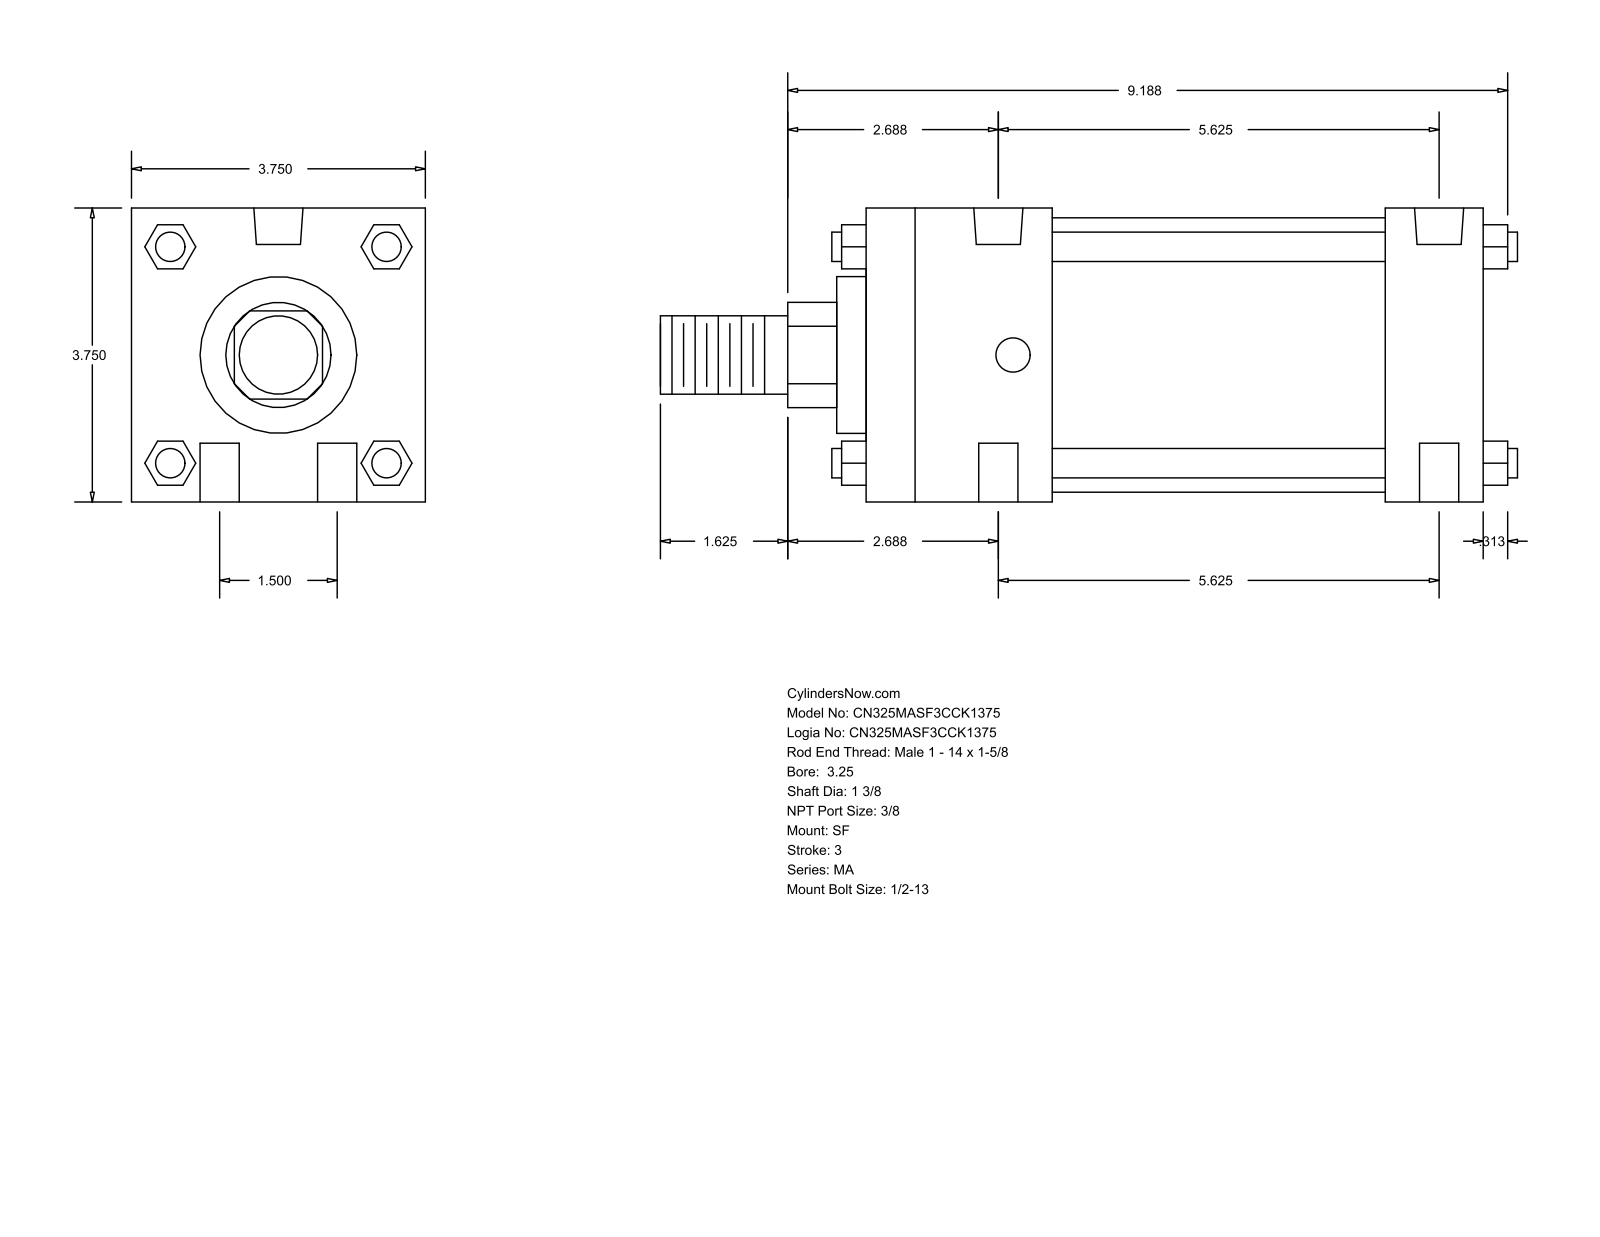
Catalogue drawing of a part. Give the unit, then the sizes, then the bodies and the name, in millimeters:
Units: millimetres
Overall size (bounding box): 277.81 × 95.25 × 95.25
Round holes (diameter × count): ⌀12.7 ×4, ⌀11.11 ×2, ⌀15.93 ×2
Round bosses / shafts (diameter × count): ⌀9.53 ×4, ⌀88.9 ×1, ⌀50.8 ×1, ⌀34.92 ×1, ⌀25.4 ×1
Partial cylindrical surfaces — rounded edges, fillets, slot ends (radius × count): R17.06 ×1
Main face-to-face distances: 95.24, 200.03, 168.28, 31.75, 60.32, 107.96, 139.71, 9.52, 69.84, 177.8
Hole centre spacings: 19.05, 144.14, 142.88, 38.1, 147.87, 133.35
Bodies: 0 solids, 124 faces (94 planar, 30 cylindrical, 0 other)
Part name (STEP PRODUCT): MA_SF__0325_1.375
STEP written by: GSSL Pune (CONFIG_CONTROL_DESIGN)
